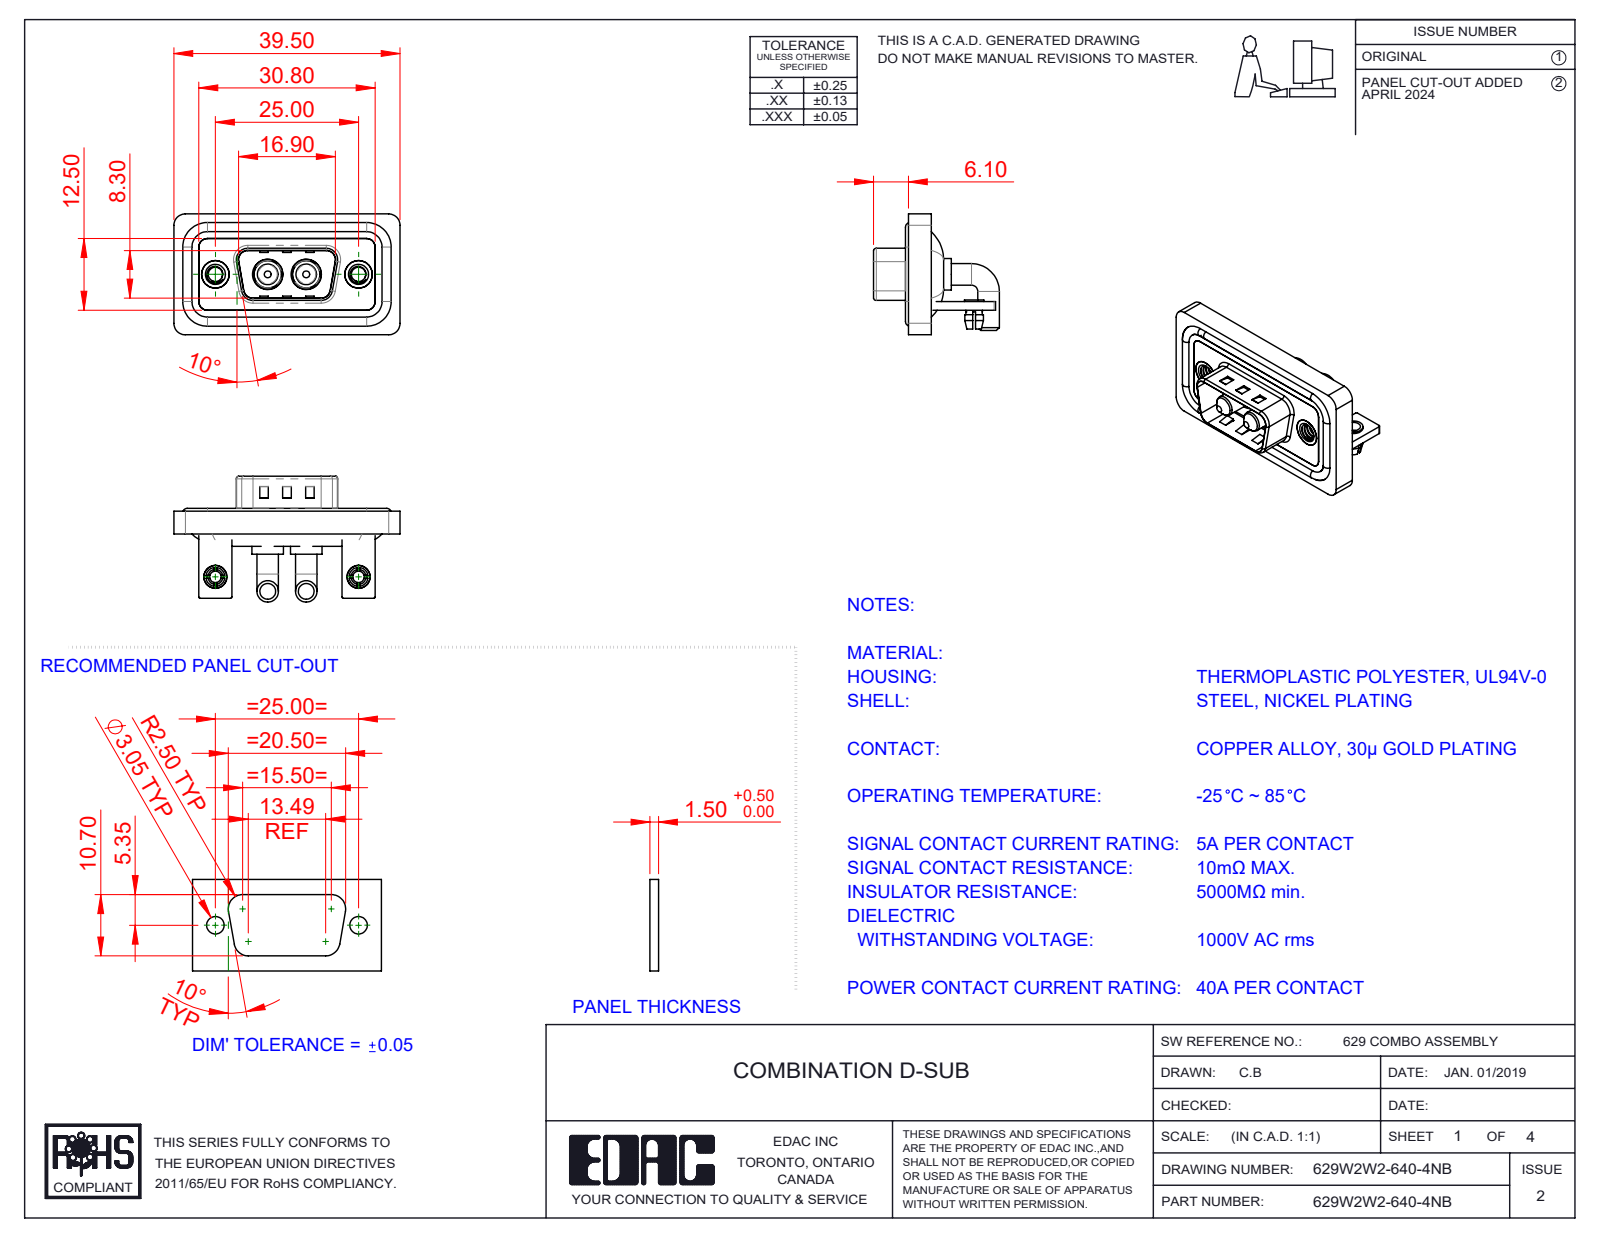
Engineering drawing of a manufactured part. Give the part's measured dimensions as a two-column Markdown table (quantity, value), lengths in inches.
| quantity | value |
| --- | --- |
| part name | 629Combo Housing_2W2; 629W2W2-640-4NB; 629Combo Waterproof Housing_09 Contacts; 629Combo Threaded Rivet_B (+5 more) |
| STEP written by | SolidWorks 2023 (CONFIG_CONTROL_DESIGN) |
| units | inches |
| bodies | 15 solids, 627 faces (233 planar, 272 cylindrical, 122 other) |
| overall size | 1.555 × 0.865 × 0.831 |
| volume | 0.307 in³ |
| surface area | 12.48 in² |
| round holes (diameter × count) | 0.098 × 4, 0.079 × 2, 0.126 × 2, 0.157 × 2, 0.189 × 2, 0.191 × 2, 0.197 × 2, 0.209 × 2 |
| round bosses / shafts (diameter × count) | 0.148 × 4, 0.063 × 4, 0.217 × 2, 0.205 × 2, 0.193 × 2, 0.187 × 2, 0.157 × 2, 0.142 × 2 |
| partial cylindrical surfaces (radius × count) | 0.079 × 19, 0.059 × 18, 0.01 × 16, 0.02 × 9, 0.063 × 8, 0.024 × 4, 0.026 × 4, 0.035 × 4 |
| main face-to-face distances | 0.016, 0.059, 0.114, 0.031, 0.043, 0.047, 0.083, 0.063, 0.146, 0.098 |
| hole center spacings | 0.36, 0.624, 0.984, 0.265 |
